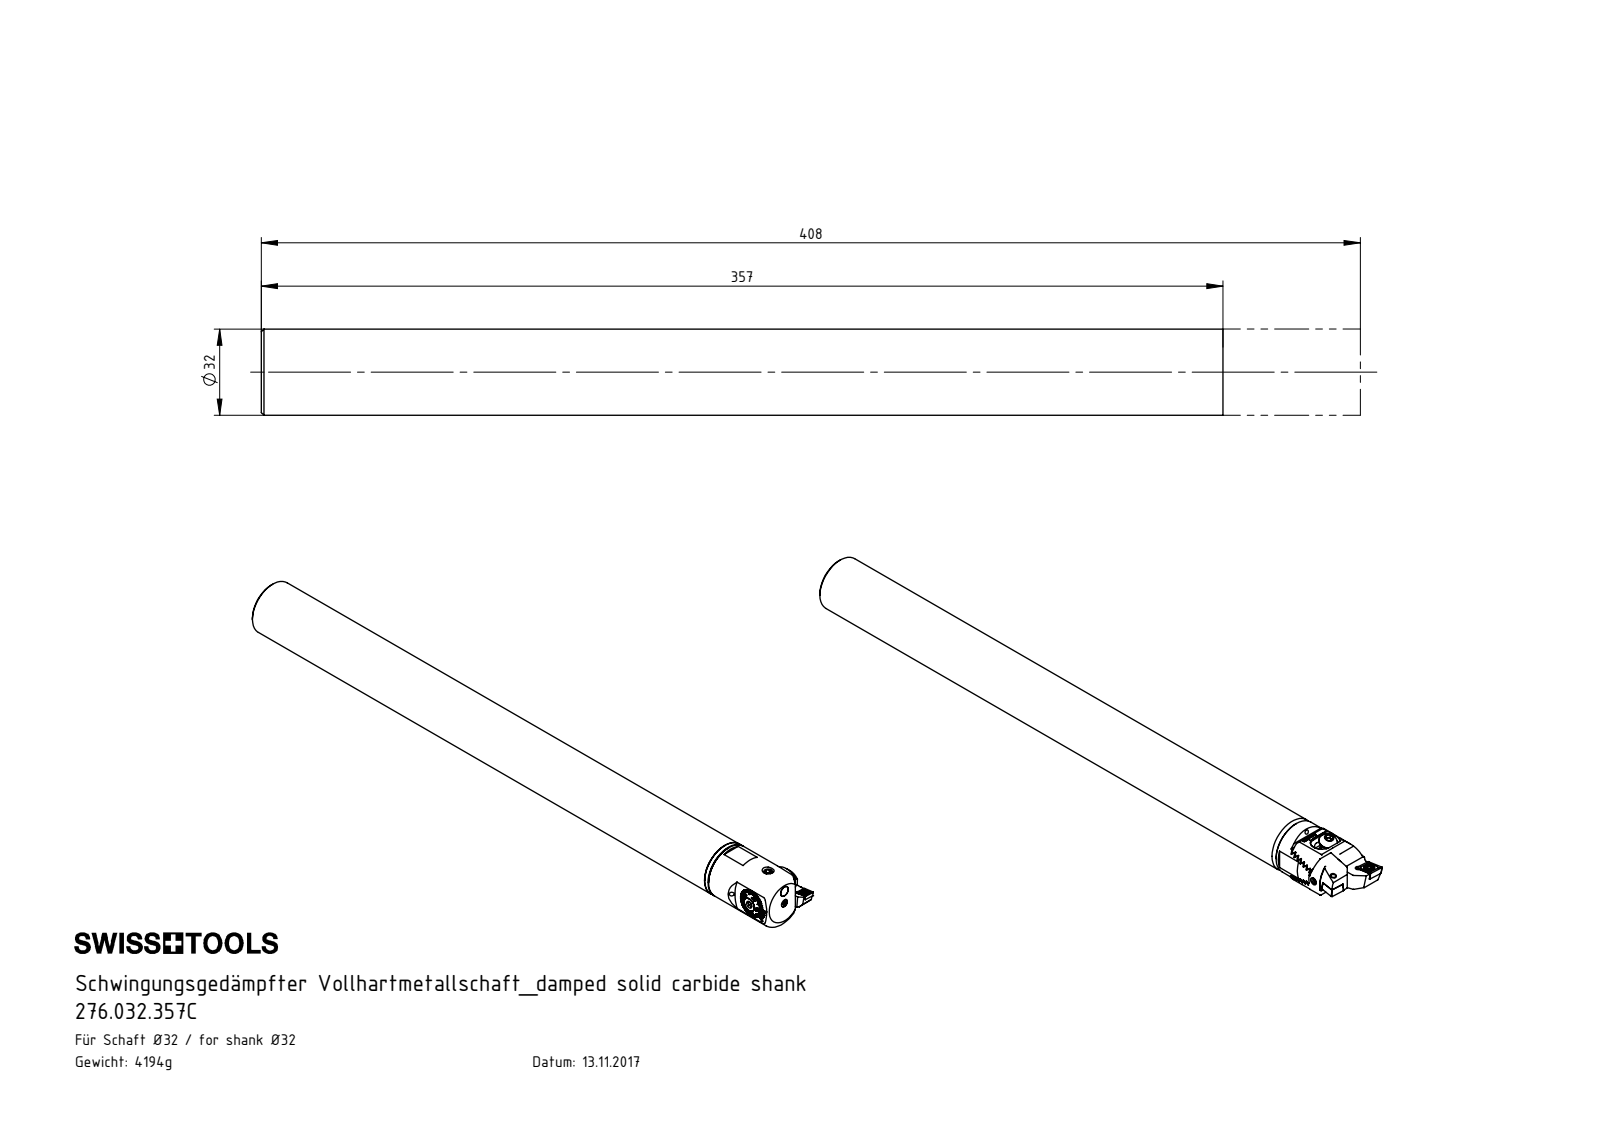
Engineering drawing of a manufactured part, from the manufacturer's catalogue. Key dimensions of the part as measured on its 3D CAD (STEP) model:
Part name (STEP PRODUCT): 276.032.357C; HP5-ER1.019.036_A; HP5-Z32.040.051_fr Zeichnung; Z32-WCB.001.021 (+8 more)
STEP written by: SolidWorks 2017 (CONFIG_CONTROL_DESIGN)
Units: millimetres
Bodies: 16 solids, 976 faces (446 planar, 238 cylindrical, 292 other)
Overall size (bounding box): 408 × 40 × 32
Volume: 303 486 mm³ · Surface area: 63 883 mm²
Round holes (diameter × count): ⌀2.5 ×5, ⌀3.3 ×4, ⌀1.6 ×2, ⌀2 ×2, ⌀4.4 ×2, ⌀5 ×2, ⌀6.1 ×2, ⌀6.4 ×2, ⌀6.8 ×2, ⌀3.5 ×1, ⌀4.2 ×1, ⌀10.2 ×1
Round bosses / shafts (diameter × count): ⌀4 ×4, ⌀10.5 ×2, ⌀10.2 ×2, ⌀6 ×2, ⌀5.25 ×2, ⌀32 ×1, ⌀3 ×1, ⌀2.2 ×1
Partial cylindrical surfaces — rounded edges, fillets, slot ends (radius × count): R0.5 ×16, R0.2 ×14, R0.2 ×12, R0.34 ×12, R0.59 ×12, R2 ×4, R3.3 ×4, R6 ×4
Main face-to-face distances: 2.38, 4.76, 7.14, 3, 357, 360, 9.52, 36, 39, 321
Hole centre spacings: 6.07, 6.19, 24.22, 24.33, 28.65, 9, 9.01, 17.39
